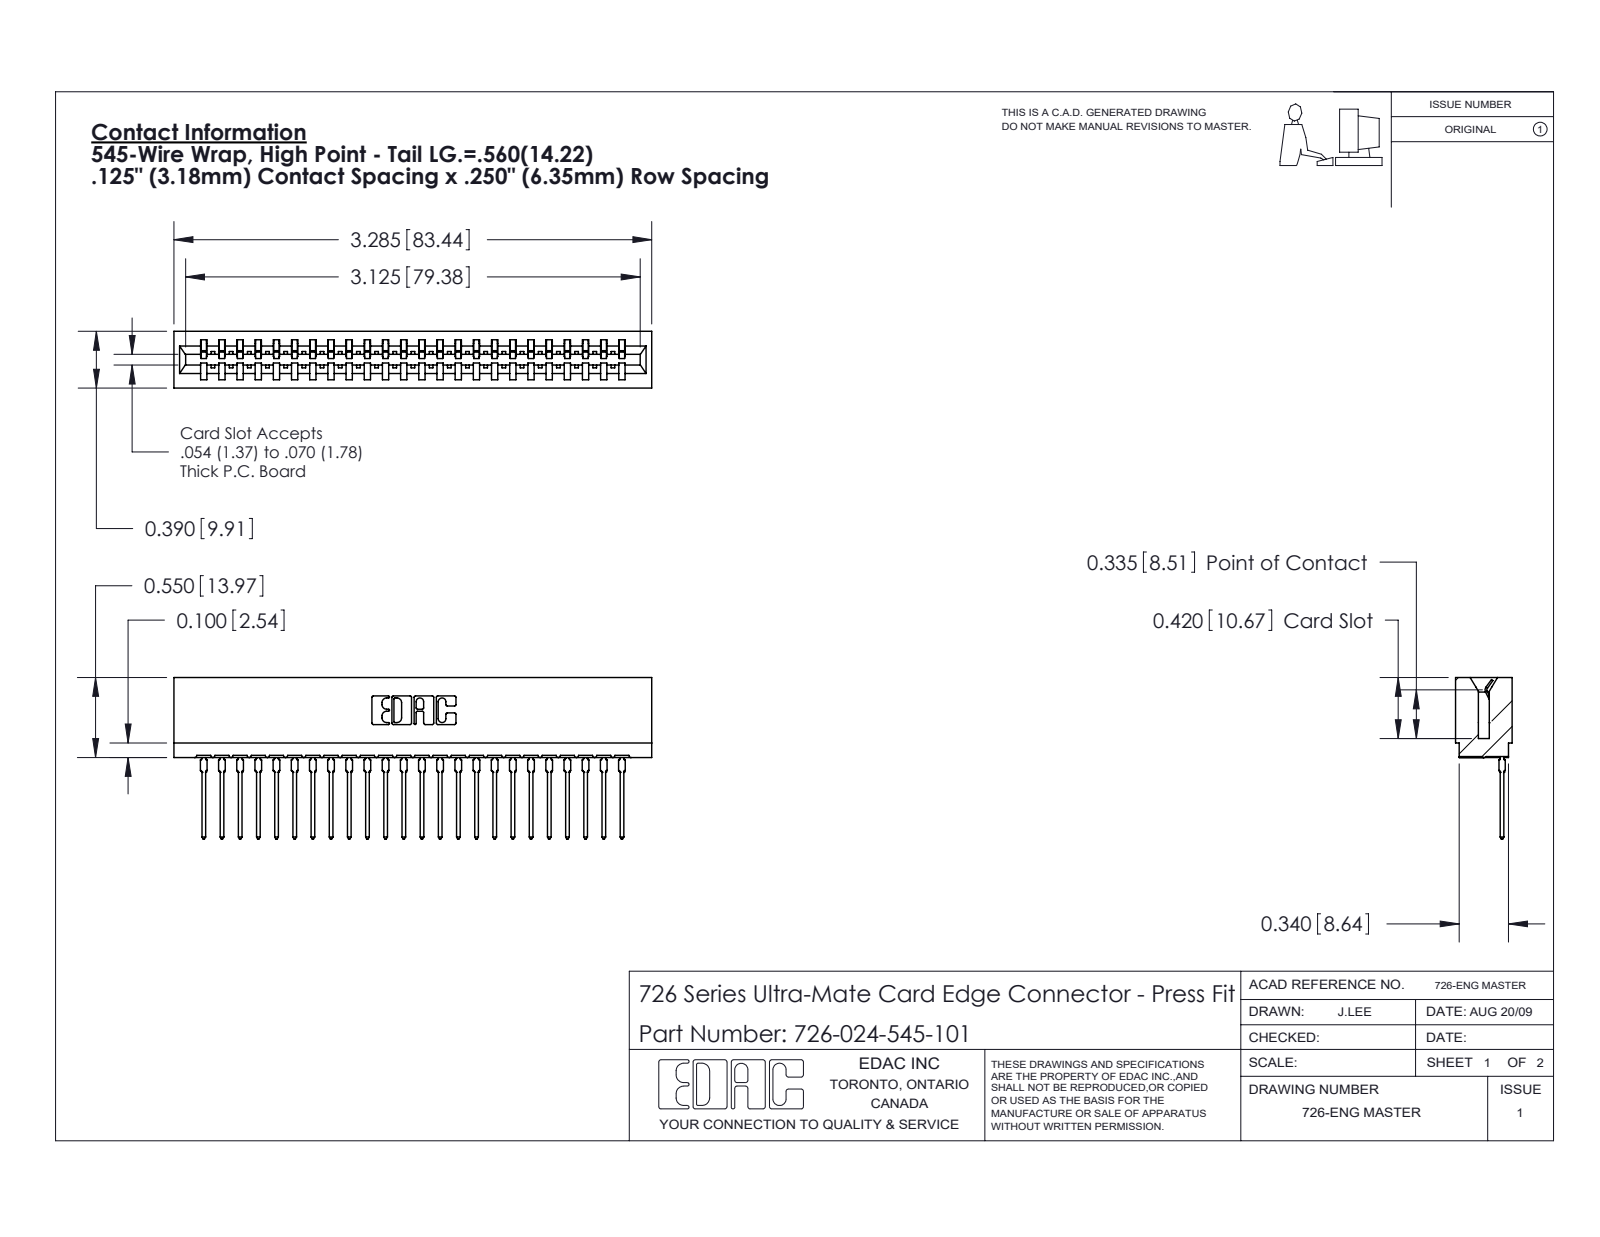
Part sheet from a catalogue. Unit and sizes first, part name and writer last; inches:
Units: inches
Overall size (bounding box): 3.285 × 1.109 × 0.39
Partial cylindrical surfaces — rounded edges, fillets, slot ends (radius × count): R0.021 ×48, R0.015 ×25, R0.01 ×22, R0.007 ×6, R0.031 ×6, R0.005 ×4, R0.011 ×4, R0.026 ×3
Main face-to-face distances: 0.057, 0.333, 0.39, 0.025, 0.25, 0.307, 0.083, 0.042, 0.75, 0.275
Volume: 0.465 in³ · Surface area: 18.13 in²
Bodies: 25 solids, 2689 faces (1567 planar, 498 cylindrical, 624 other)
Part name (STEP PRODUCT): 746-292-001_545; 726-024-545-101; 726 Part_.515 Slot Depth - 01
STEP written by: SolidWorks 2020 (CONFIG_CONTROL_DESIGN)
